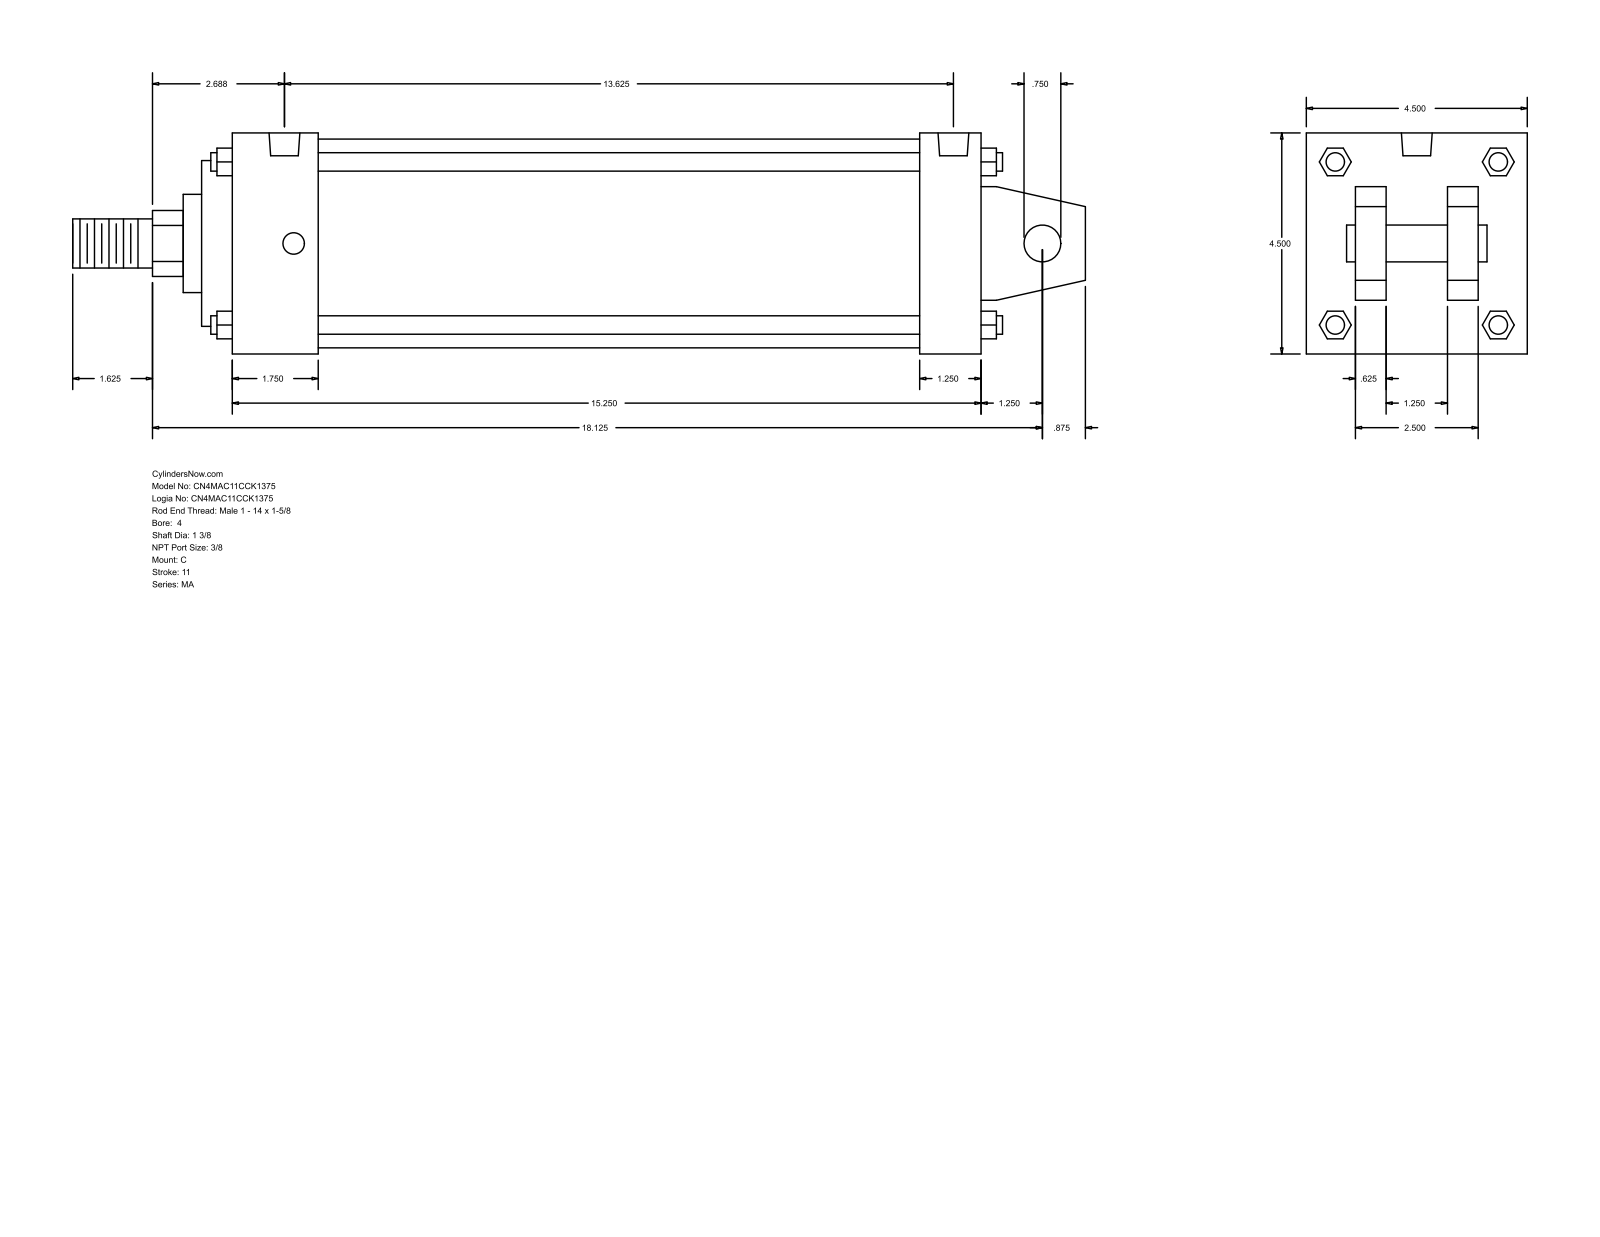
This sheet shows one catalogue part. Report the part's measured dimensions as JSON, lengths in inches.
{"part_name": "MA_C__0400_1.375", "step_written_by": "GSSL Pune (CONFIG_CONTROL_DESIGN)", "units": "inches", "bodies": {"solids": 0, "faces": 141, "planar": 109, "cylindrical": 32, "other": 0}, "overall_size": [20.625, 4.5, 4.5], "round_holes": [[0.437, 4], [0.627, 2]], "round_bosses_or_shafts": [[0.375, 4], [4.25, 1], [3.375, 1], [2, 1], [1.375, 1], [1, 1], [0.75, 1]], "partial_cylinders_radius": [[0.672, 1]], "face_to_face_distances": [4.5, 0.625, 15.25, 2.875, 1.625, 1, 3.5, 1.875, 15.875, 14.625], "hole_center_spacings": [0.188, 13.25, 13.437, 13.625]}
